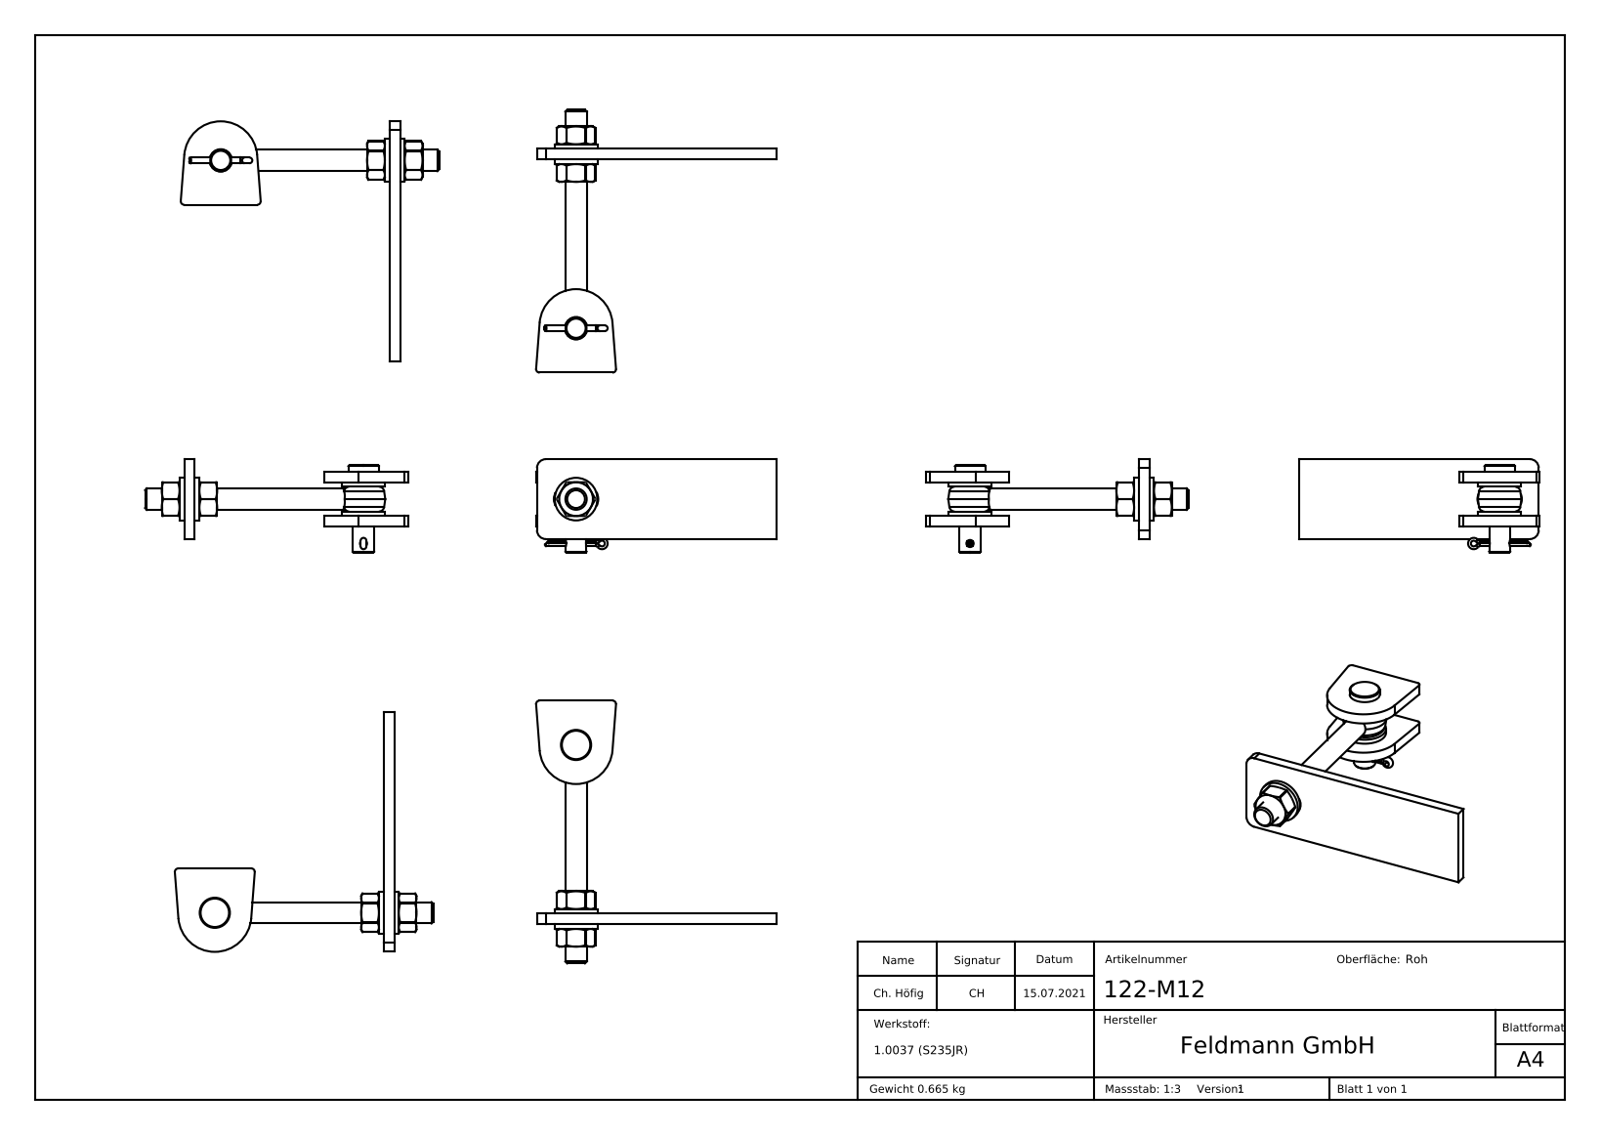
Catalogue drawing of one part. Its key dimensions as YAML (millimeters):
part_name: "Torband Teil1; 121-Mxx Teil6; Torband Teil2_122-M12 Teil2; Torband Teil4 (+8 more)"
step_written_by: "SolidWorks 2018 (CONFIG_CONTROL_DESIGN)"
units: millimeters
bodies: {solids: 12, faces: 403, planar: 179, cylindrical: 84, other: 140}
overall_size: [24000, 14000, 14000]
volume: 85216
surface_area: 38908
round_holes:
  - {diameter: 13, count: 2}
  - {diameter: 4, count: 1}
  - {diameter: 10.2, count: 1}
  - {diameter: 12.3, count: 1}
  - {diameter: 12.6, count: 1}
round_bosses_or_shafts:
  - {diameter: 24, count: 2}
  - {diameter: 17, count: 1}
  - {diameter: 12, count: 1}
  - {diameter: 11.8, count: 1}
  - {diameter: 3.2, count: 1}
partial_cylinders:
  - {radius: 0.5, count: 6}
  - {radius: 1, count: 2}
  - {radius: 2, count: 2}
  - {radius: 2.59, count: 2}
  - {radius: 5, count: 2}
  - {radius: 7.5, count: 2}
  - {radius: 1.61, count: 1}
  - {radius: 6.25, count: 1}
face_to_face_distances: [6, 25.2, 19.2, 8.6, 2.6, 31.2, 6.9, 12.9, 32.1, 38.1]
